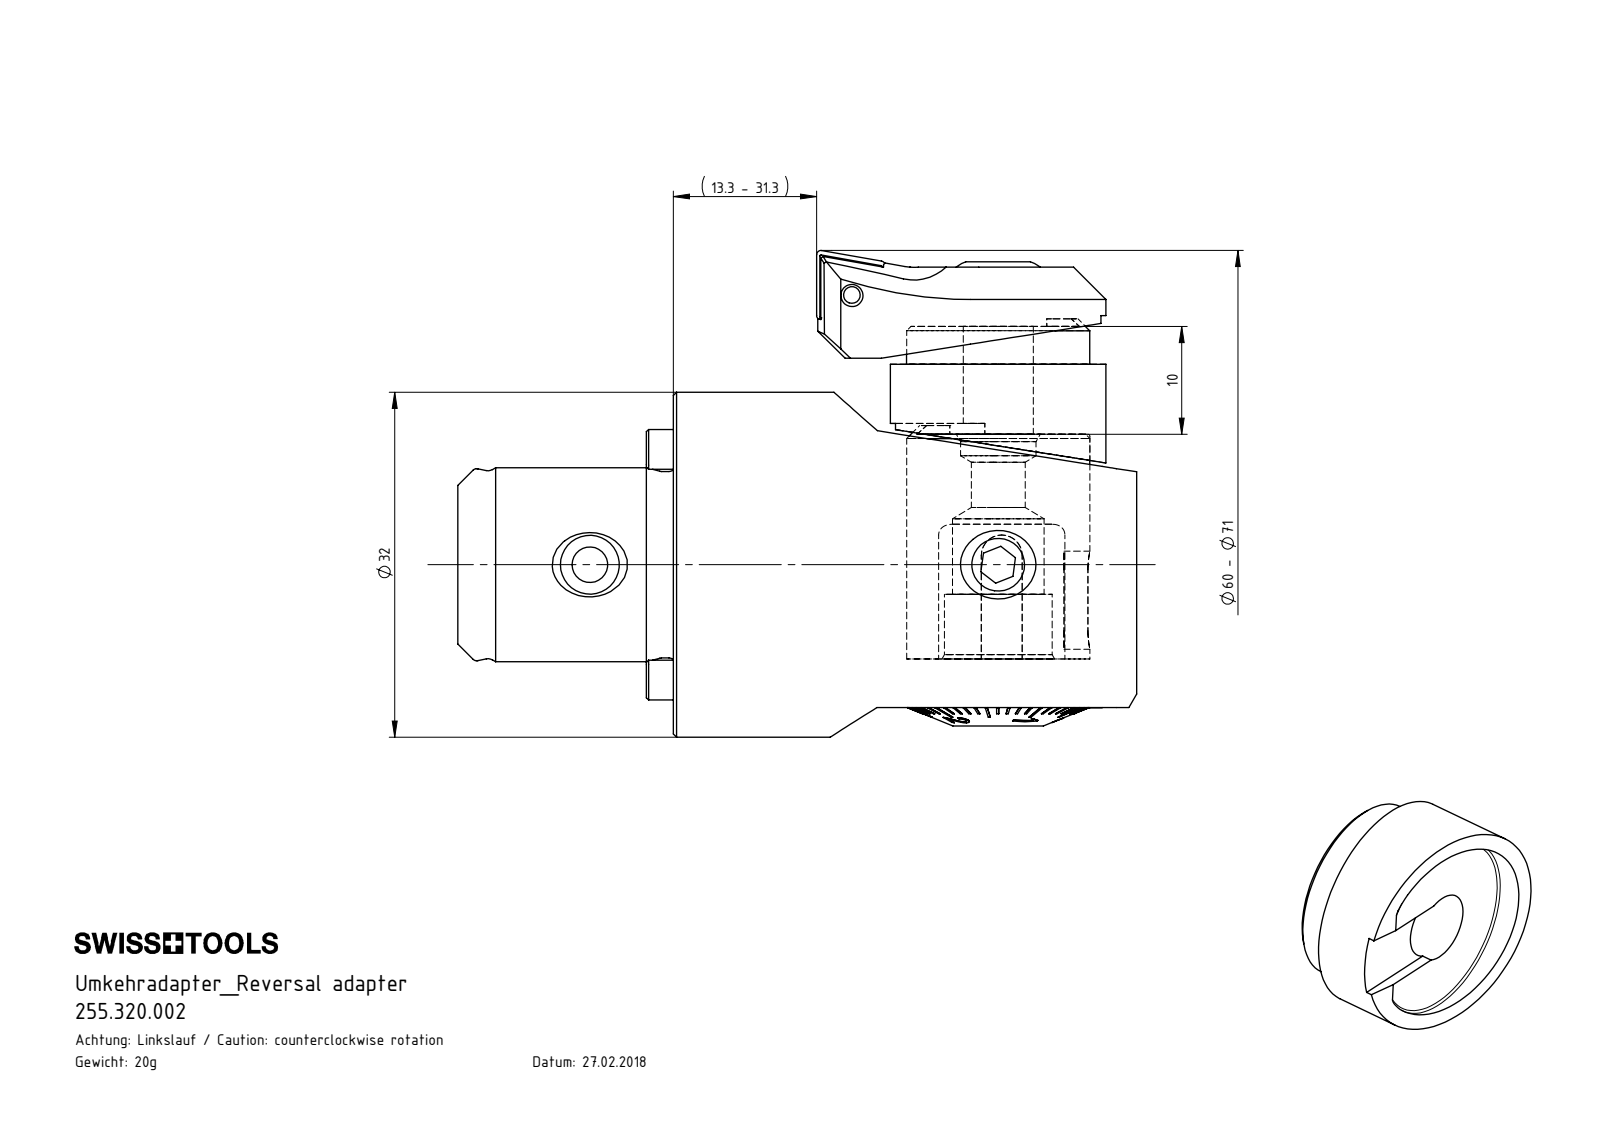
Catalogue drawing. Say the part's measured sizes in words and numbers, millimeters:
The part is named "255.320.002; F32-U00.001.010_B". Its 3-D file was written by "SolidWorks 2017 (CONFIG_CONTROL_DESIGN)". It is 1 solid with 27 faces: 11 planar, 11 cylindrical and 5 other. Overall it measures 20 by 20 by 13.37 millimeters. Its volume is 2 568 cubic millimeters and its surface area 1 488 square millimeters. Round holes: 1 of diameter 6.5, 1 of diameter 17. Round bosses or shafts: 1 of diameter 20. Partial cylindrical surfaces (rounded edges, fillets, slot ends): 2 of radius 0.5. The main face-to-face distances are 10, 6.5, 3.5, 1, 5.5, 9, 10.7, 9.7, 4.2, 0.7.
